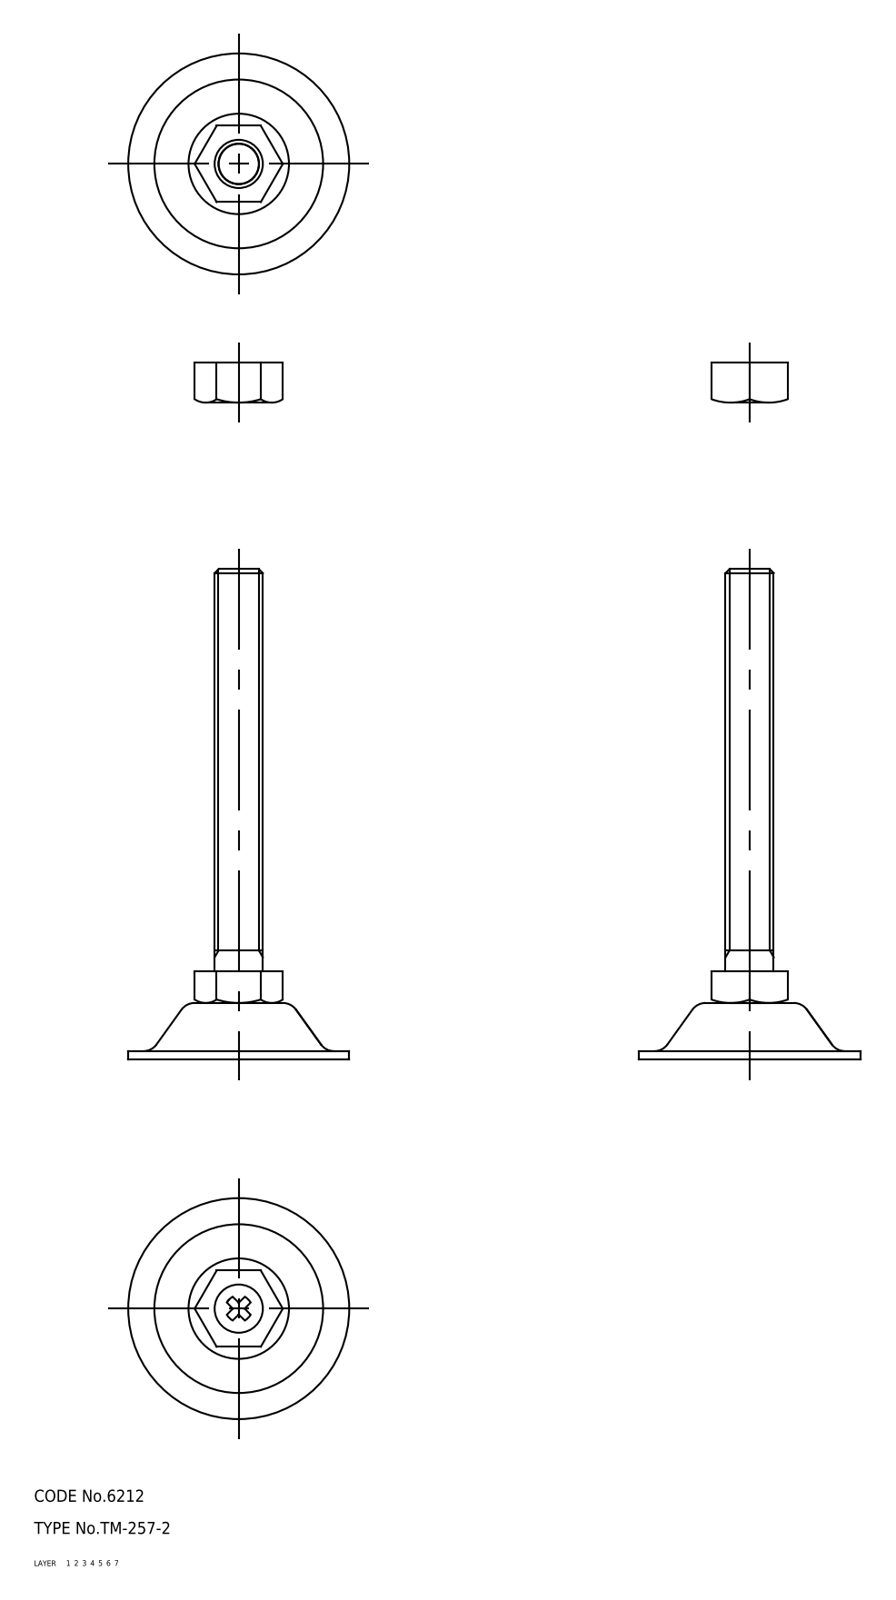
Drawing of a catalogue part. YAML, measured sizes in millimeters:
part_name: "nut; foot; bolt; TM_257_2_9727_36"
step_written_by: "CADfix (AUTOMOTIVE_DESIGN)"
units: millimeters
bodies: {solids: 4, faces: 95, planar: 0, cylindrical: 0, other: 95}
overall_size: [122, 55, 55]
volume: 24831
surface_area: 14357
